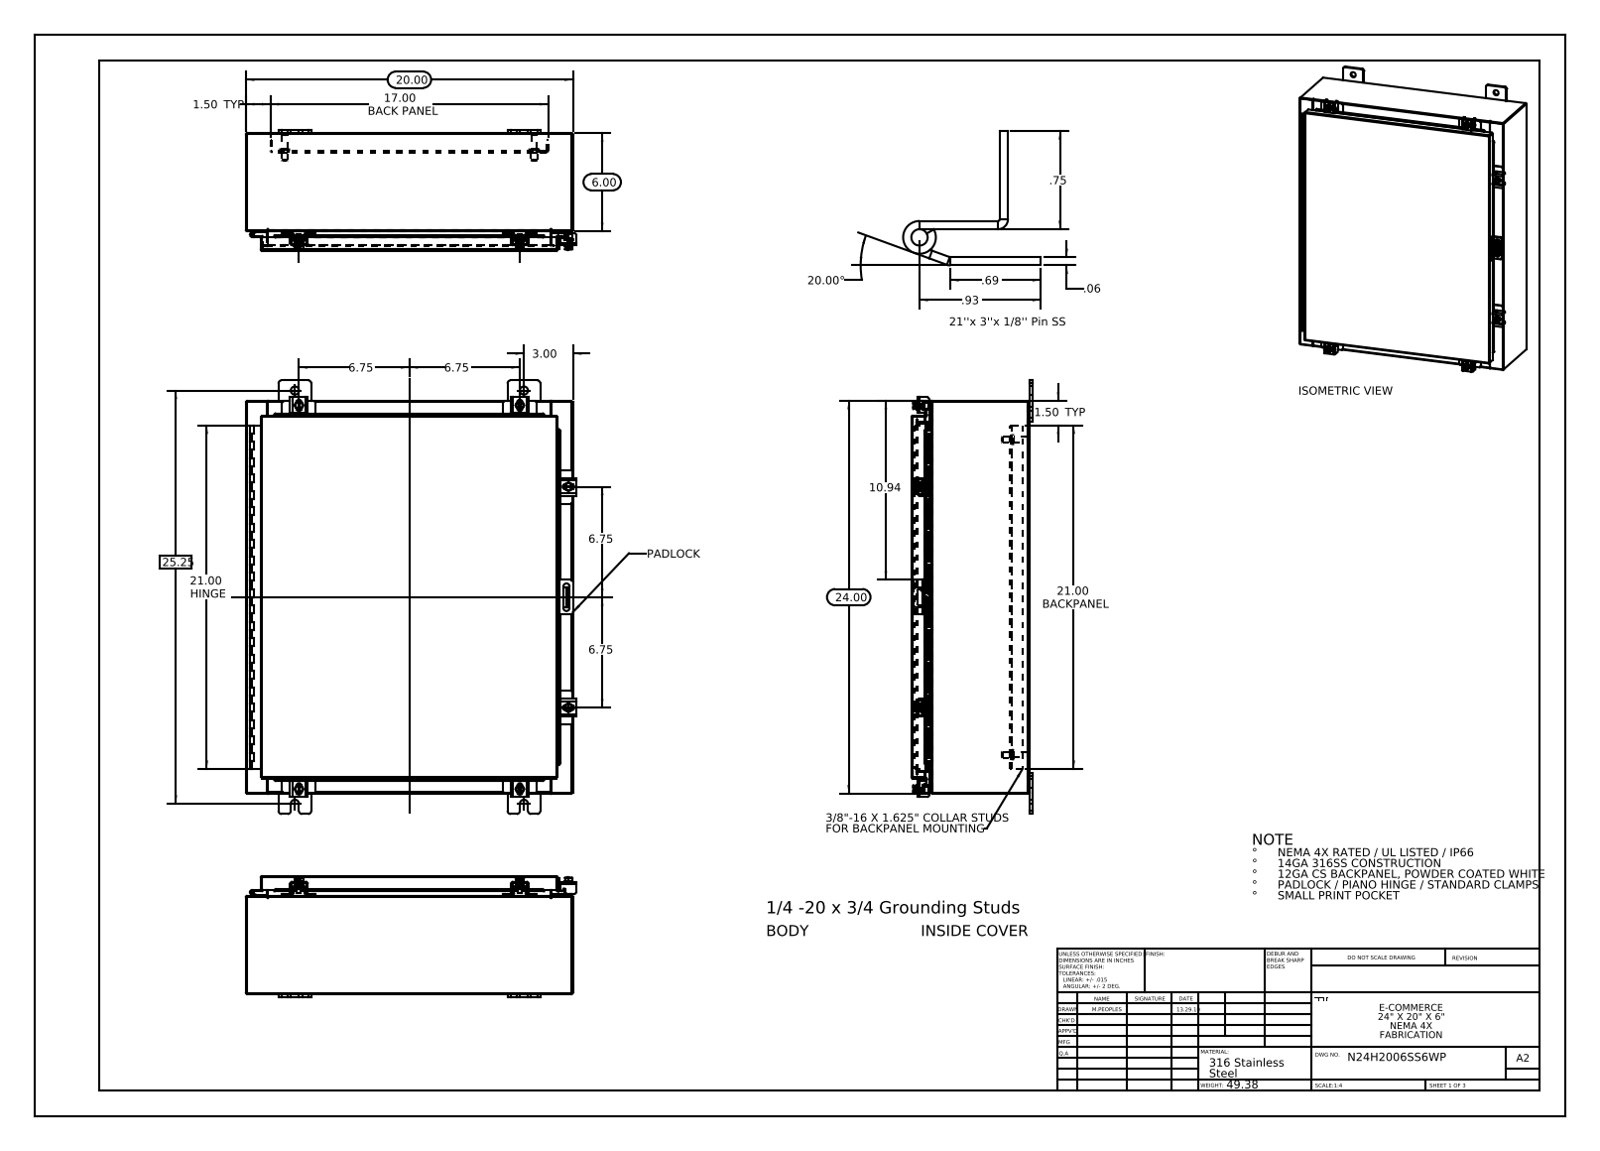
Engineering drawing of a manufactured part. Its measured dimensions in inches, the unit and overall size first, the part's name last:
Units: inches
Overall size (bounding box): 26.5 × 20.211 × 7.389
Round holes (diameter × count): ⌀0.5 ×8, ⌀0.213 ×6, ⌀0.26 ×6, ⌀0.125 ×2, ⌀0.125 ×1
Round bosses / shafts (diameter × count): ⌀0.25 ×7, ⌀0.5 ×6, ⌀0.399 ×6, ⌀0.625 ×4, ⌀0.375 ×4, ⌀0.33 ×4
Partial cylindrical surfaces — rounded edges, fillets, slot ends (radius × count): R0.06 ×30, R0.013 ×25, R0.19 ×24, R0.088 ×21, R0.12 ×12, R0.141 ×12, R0.125 ×10, R0.05 ×9
Main face-to-face distances: 0.075, 7.126, 7.201, 7.051, 0.104, 1, 1.075, 6.051, 6.126, 1.179
Hole centre spacings: 21.369, 25.739, 13.5, 0.431, 0.934, 1.858, 2.275, 2.276
Volume: 173.9 in³ · Surface area: 4 361 in²
Bodies: 47 solids, 1709 faces (908 planar, 705 cylindrical, 96 other)
Part name (STEP PRODUCT): N24H2006SS6WP Hinge Cover Side; N24H2006SS6WP 125 Pin Hinge; N24H2006SS6WP Mounting Studs; N24H2006SS6WP Mounting Feet (+8 more)
STEP written by: SolidWorks 2013 (CONFIG_CONTROL_DESIGN)
